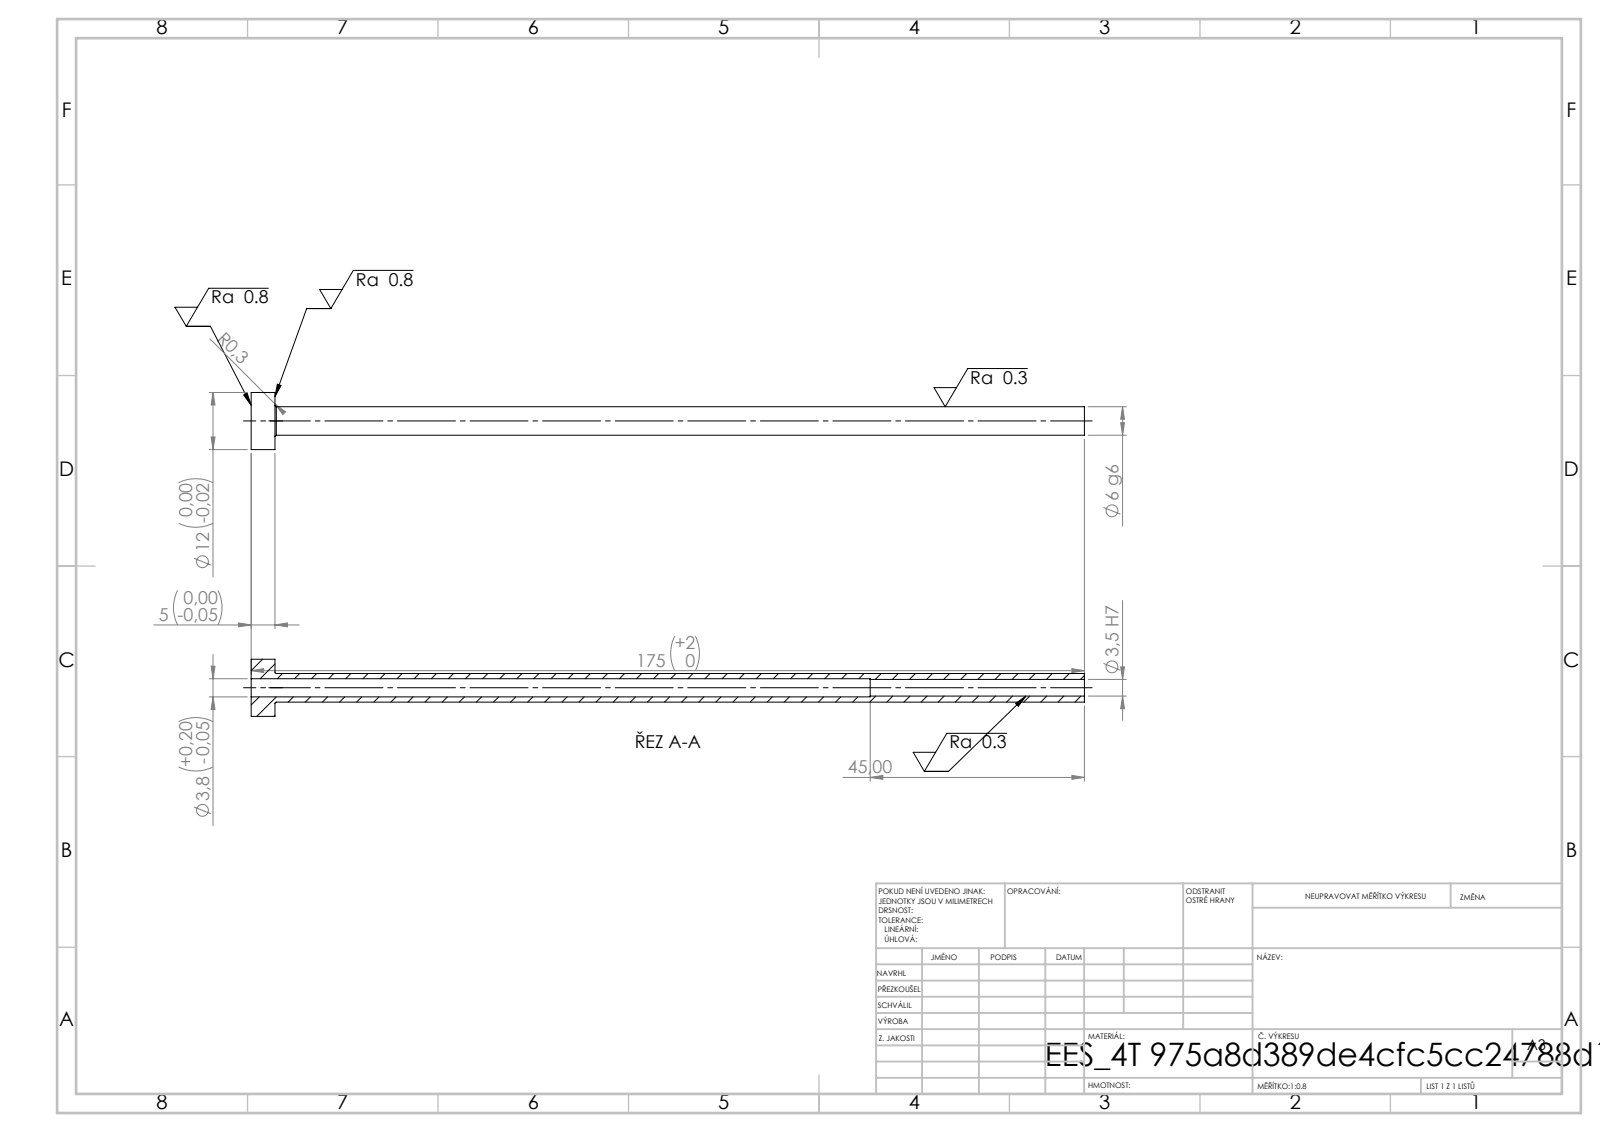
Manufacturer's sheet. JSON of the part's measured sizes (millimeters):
{"step_written_by": "SolidWorks 2019 (CONFIG_CONTROL_DESIGN)", "units": "millimeters", "bodies": {"solids": 1, "faces": 14, "planar": 4, "cylindrical": 8, "other": 2}, "overall_size": [175, 12, 12], "volume_mm3": 3465, "surface_area_mm2": 5644, "round_holes": [[3.5, 1], [3.8, 1]], "round_bosses_or_shafts": [[12, 1], [6, 1]], "face_to_face_distances": [5, 175, 170, 130, 125, 45]}
